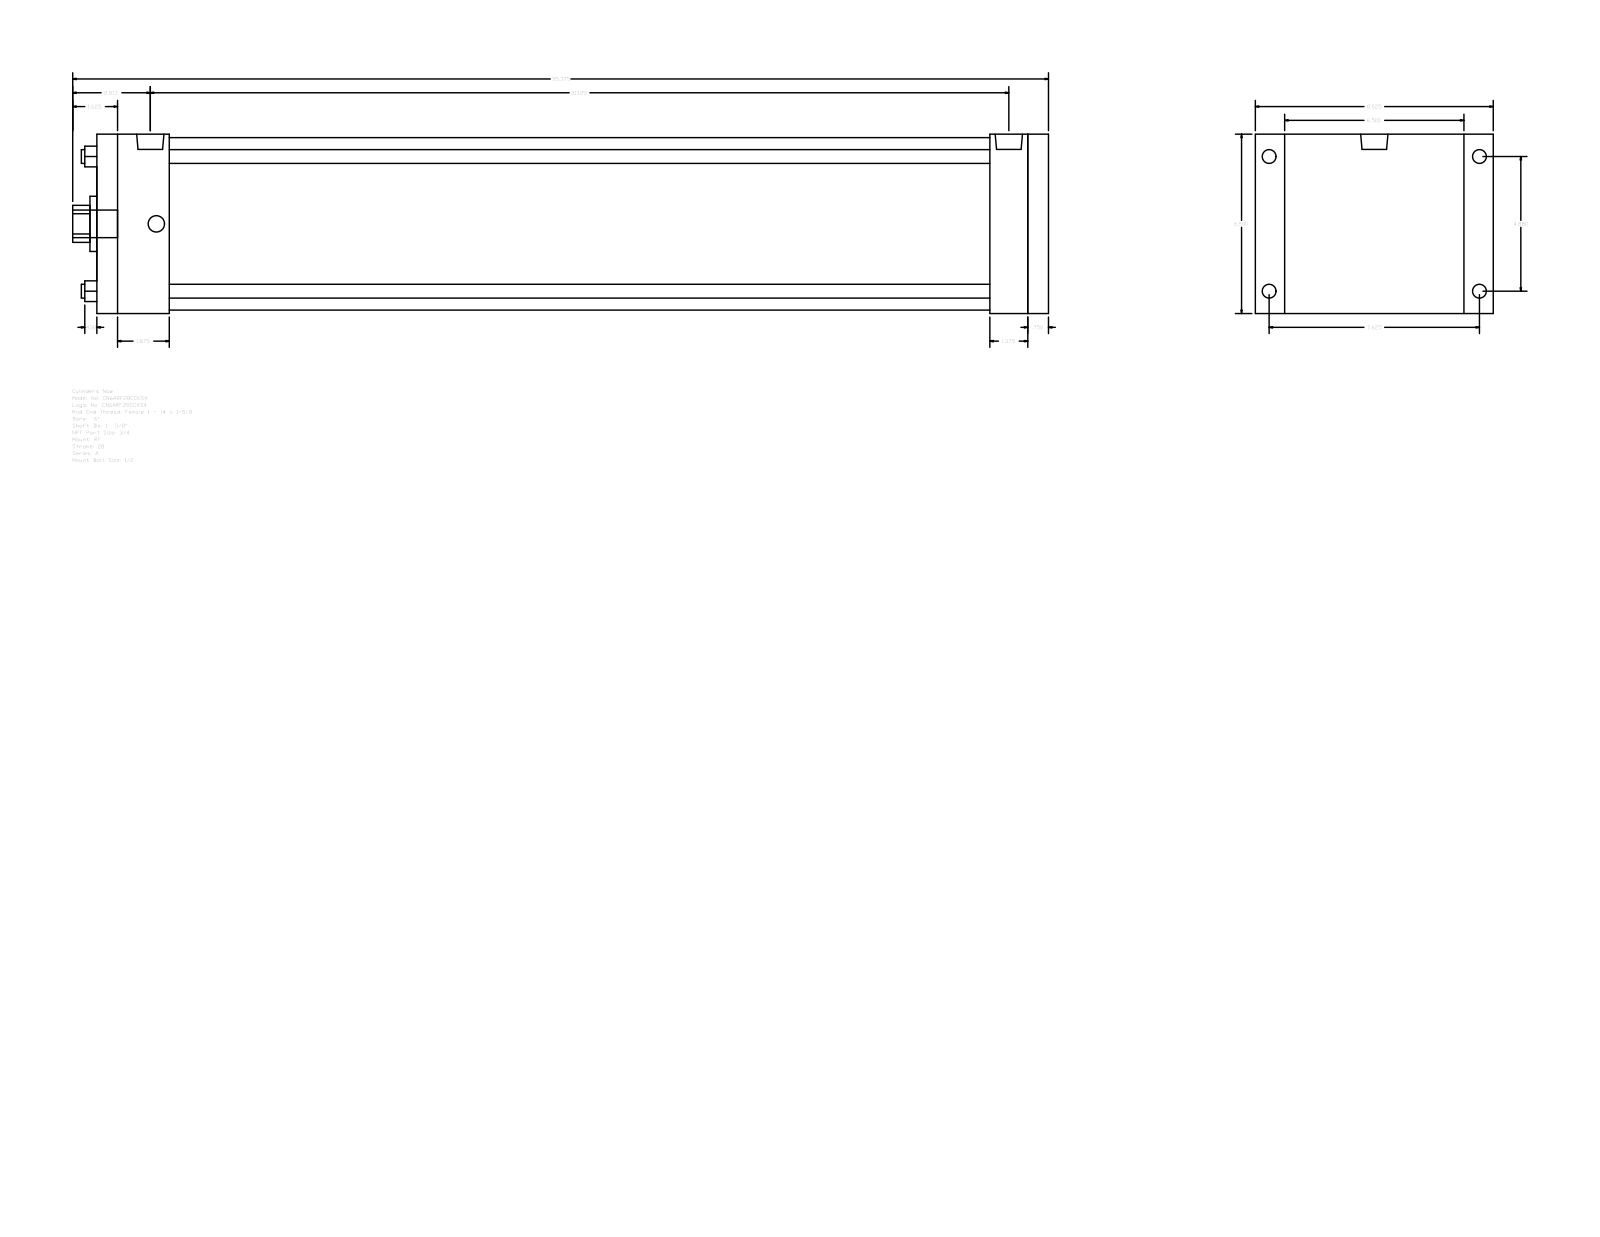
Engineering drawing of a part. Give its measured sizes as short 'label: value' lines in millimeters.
name: A_RF__0600_1.375
written by: GSSL Pune (CONFIG_CONTROL_DESIGN)
unit: mm
bodies: 0 solids, 92 faces (64 planar, 28 cylindrical, 0 other)
size: 898.52 × 219.07 × 165.1
holes: 4× ⌀12.7, 1× ⌀34.92, 1× ⌀50.8, 1× ⌀158.75
bosses: 4× ⌀15.08, 4× ⌀12.7, 2× ⌀25.12, 1× ⌀25.4
rounds: 1× R17.06
face distances: 165.1, 876.29, 19.04, 857.25, 66.67, 790.58, 809.62, 822.32, 755.65, 34.93
hole spacings: 87.65, 123.96, 175.31
